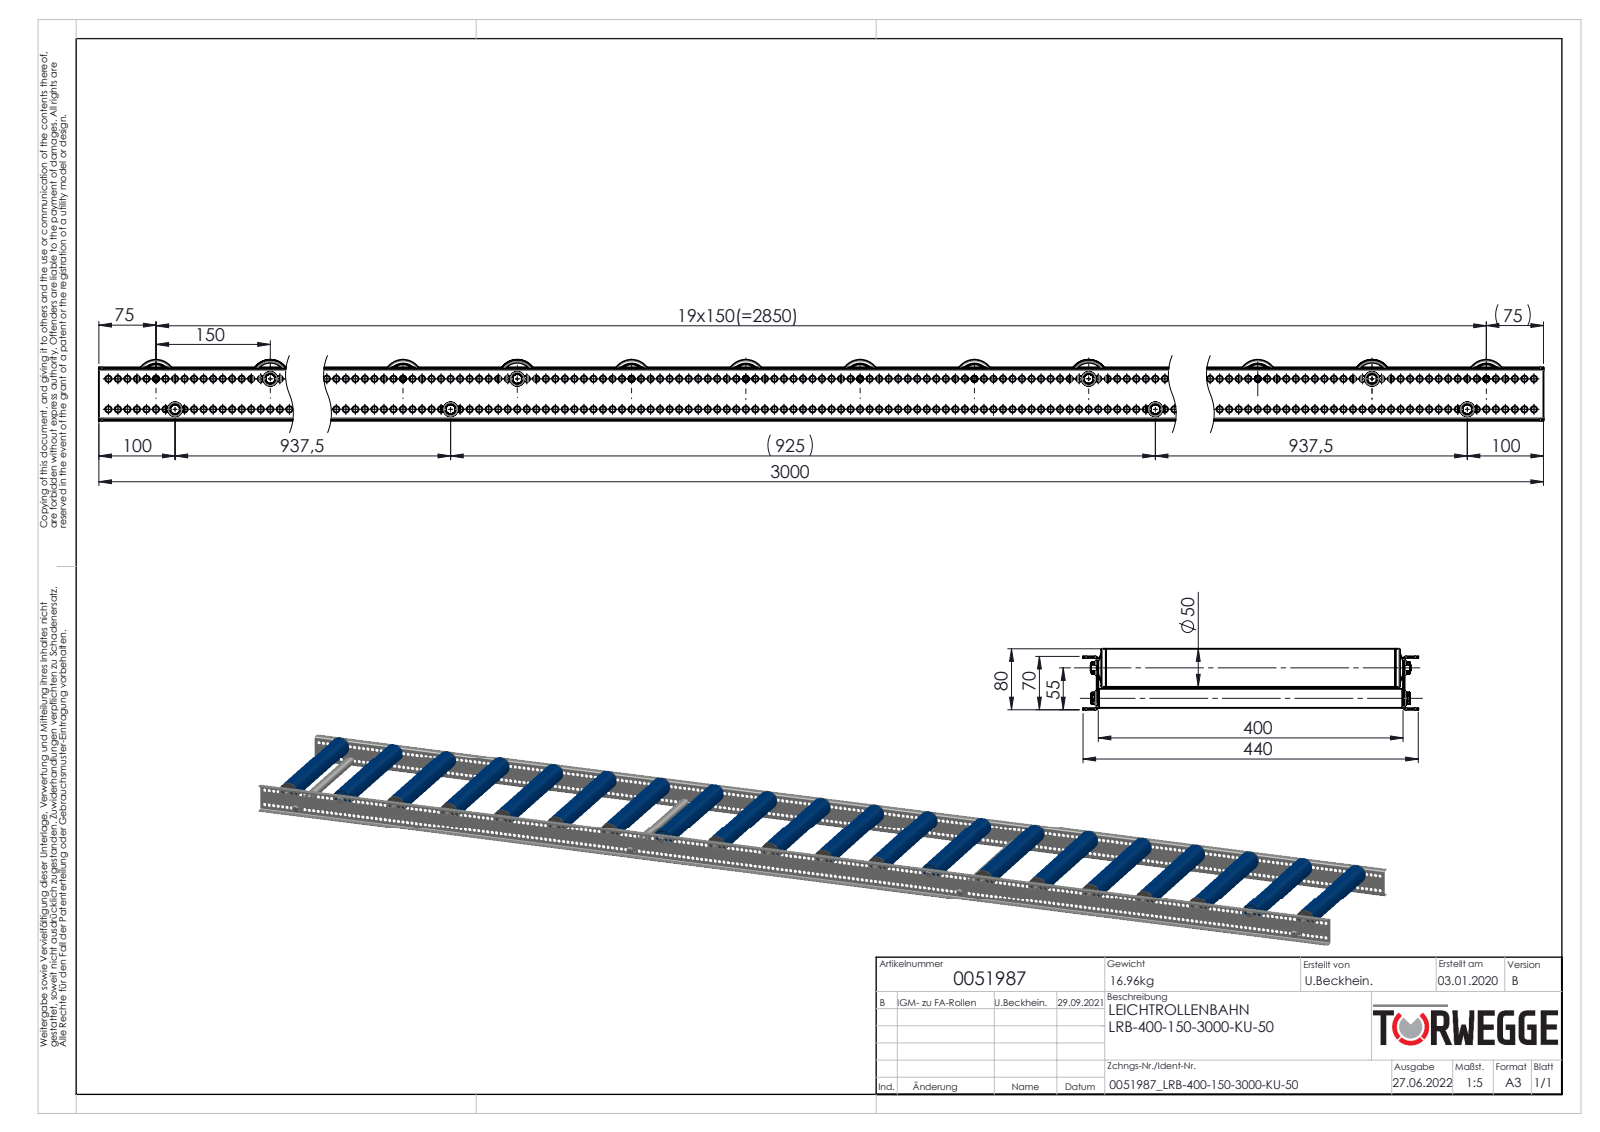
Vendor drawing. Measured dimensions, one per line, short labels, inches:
name: 0026266_Typ-KUT100-50x2,8-12; 0039780-Achse-ST-Ø12-KFG_IGM8-AL=400; Sicherungsring_DIN471_8x0.8_Circlip DIN 471 - 8 x 0.8; 0051987 (+8 more)
written by: SolidWorks 2020 (AUTOMOTIVE_DESIGN)
unit: in
bodies: 414 solids, 8500 faces (2012 planar, 3960 cylindrical, 2528 other)
size: 118.11 × 17.323 × 3.15
volume: 375.8 in³; area: 7 443 in²
holes: 478× ⌀0.323, 16× ⌀0.299, 16× ⌀0.315, 16× ⌀0.984, 16× ⌀1.181, 16× ⌀1.378, 16× ⌀1.551, 16× ⌀1.575, 8× ⌀0.268, 4× ⌀0.472, 4× ⌀0.476, 4× ⌀0.63
bosses: 20× ⌀1.969, 16× ⌀1.748, 16× ⌀1.496, 16× ⌀1.417, 16× ⌀1.299, 16× ⌀0.866, 16× ⌀0.827, 8× ⌀0.984
rounds: 32× R0.024, 32× R0.03, 32× R0.096, 16× R0.098, 16× R0.192, 16× R0.276, 8× R0.157, 4× R0.079
face distances: 0.079, 15.827, 2.677, 15.748, 15.906, 2.756, 2.598, 0.236, 15.433, 0.472
hole spacings: 0.492, 0.984, 1.476, 1.969, 2.461, 2.953, 3.445, 3.937
